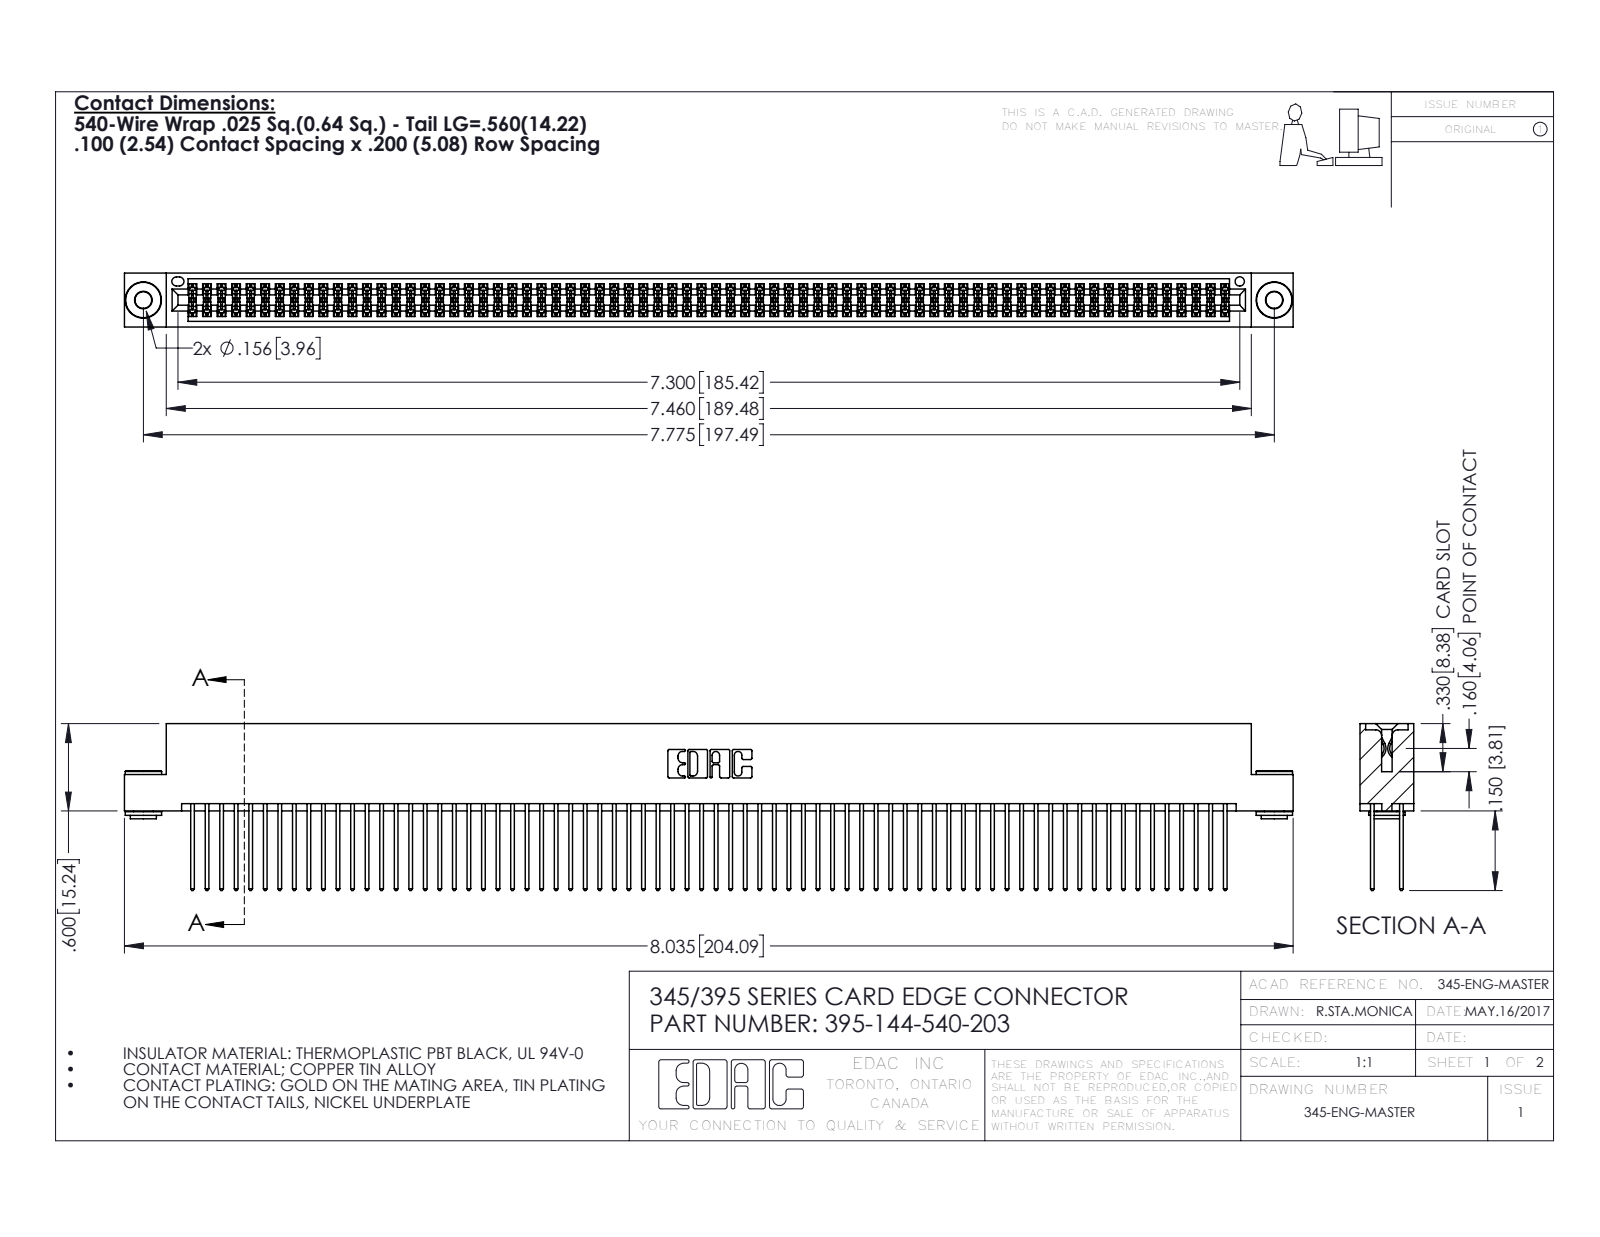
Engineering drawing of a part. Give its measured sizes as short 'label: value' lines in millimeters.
name: 345-250-002_345-250-002-102; 345 Part_Flush Mounting Lugs - 0.156 Dia-TH; 395-144-540-203; 345-292-001_345-293-140
written by: SolidWorks 2016 (CONFIG_CONTROL_DESIGN)
unit: mm
bodies: 147 solids, 7364 faces (4842 planar, 2514 cylindrical, 8 other)
size: 204.1 × 29.1 × 9.4
volume: 20 660 mm³; area: 33 870 mm²
holes: 2× ⌀2.9, 2× ⌀4, 1× ⌀1.6
bosses: 2× ⌀6.4, 2× ⌀4.6, 2× ⌀3.5
rounds: 216× R0.2, 144× R0.3, 22× R0.3, 6× R0.2, 6× R0.8, 3× R0.7, 2× R0.4, 2× R0.5
face distances: 1.8, 7.6, 5.1, 0.6, 2.5, 6.9, 5.7, 9.4, 4.4, 3.8
hole spacings: 6.9, 191.5, 197.5
